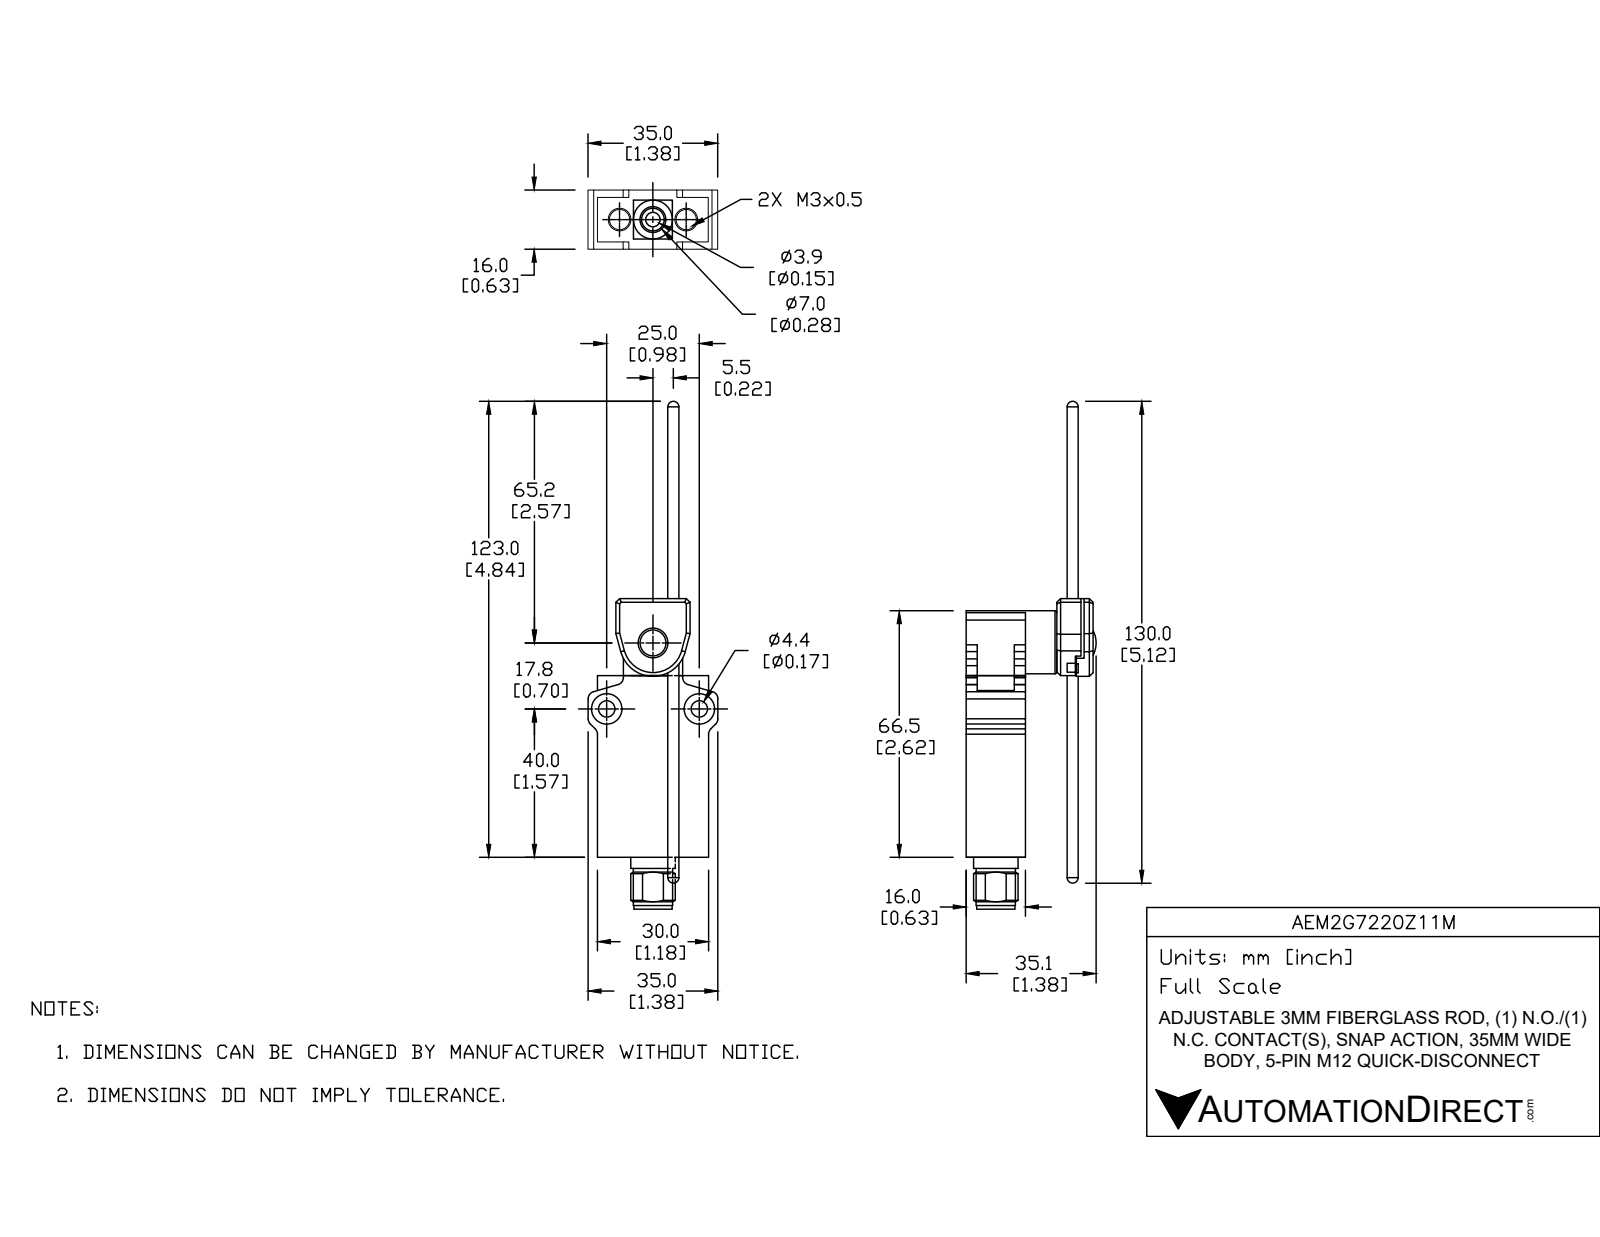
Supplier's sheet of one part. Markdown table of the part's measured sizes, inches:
| quantity | value |
| --- | --- |
| part name | AEM2G7220Z11M |
| STEP written by | SolidWorks 2017 (AUTOMOTIVE_DESIGN) |
| units | inches |
| bodies | 6 solids, 272 faces (142 planar, 85 cylindrical, 45 other) |
| overall size | 7.142 × 1.378 × 1.366 |
| volume | 2.072 in³ |
| surface area | 21.03 in² |
| round holes (diameter × count) | 0.118 × 2, 0.173 × 2, 0.323 × 2, 0.138 × 1, 0.197 × 1, 0.315 × 1 |
| round bosses / shafts (diameter × count) | 0.622 × 1, 0.472 × 1, 0.417 × 1, 0.406 × 1, 0.276 × 1, 0.118 × 1 |
| partial cylindrical surfaces (radius × count) | 0.079 × 8, 0.059 × 1, 0.173 × 1, 0.256 × 1, 0.26 × 1, 0.354 × 1 |
| main face-to-face distances | 0.63, 1.181, 0.169, 0.472, 0.28, 0.902, 0.098, 0.697, 0.988, 2.047 |
| hole center spacings | 0.866, 0.748, 0.984 |
